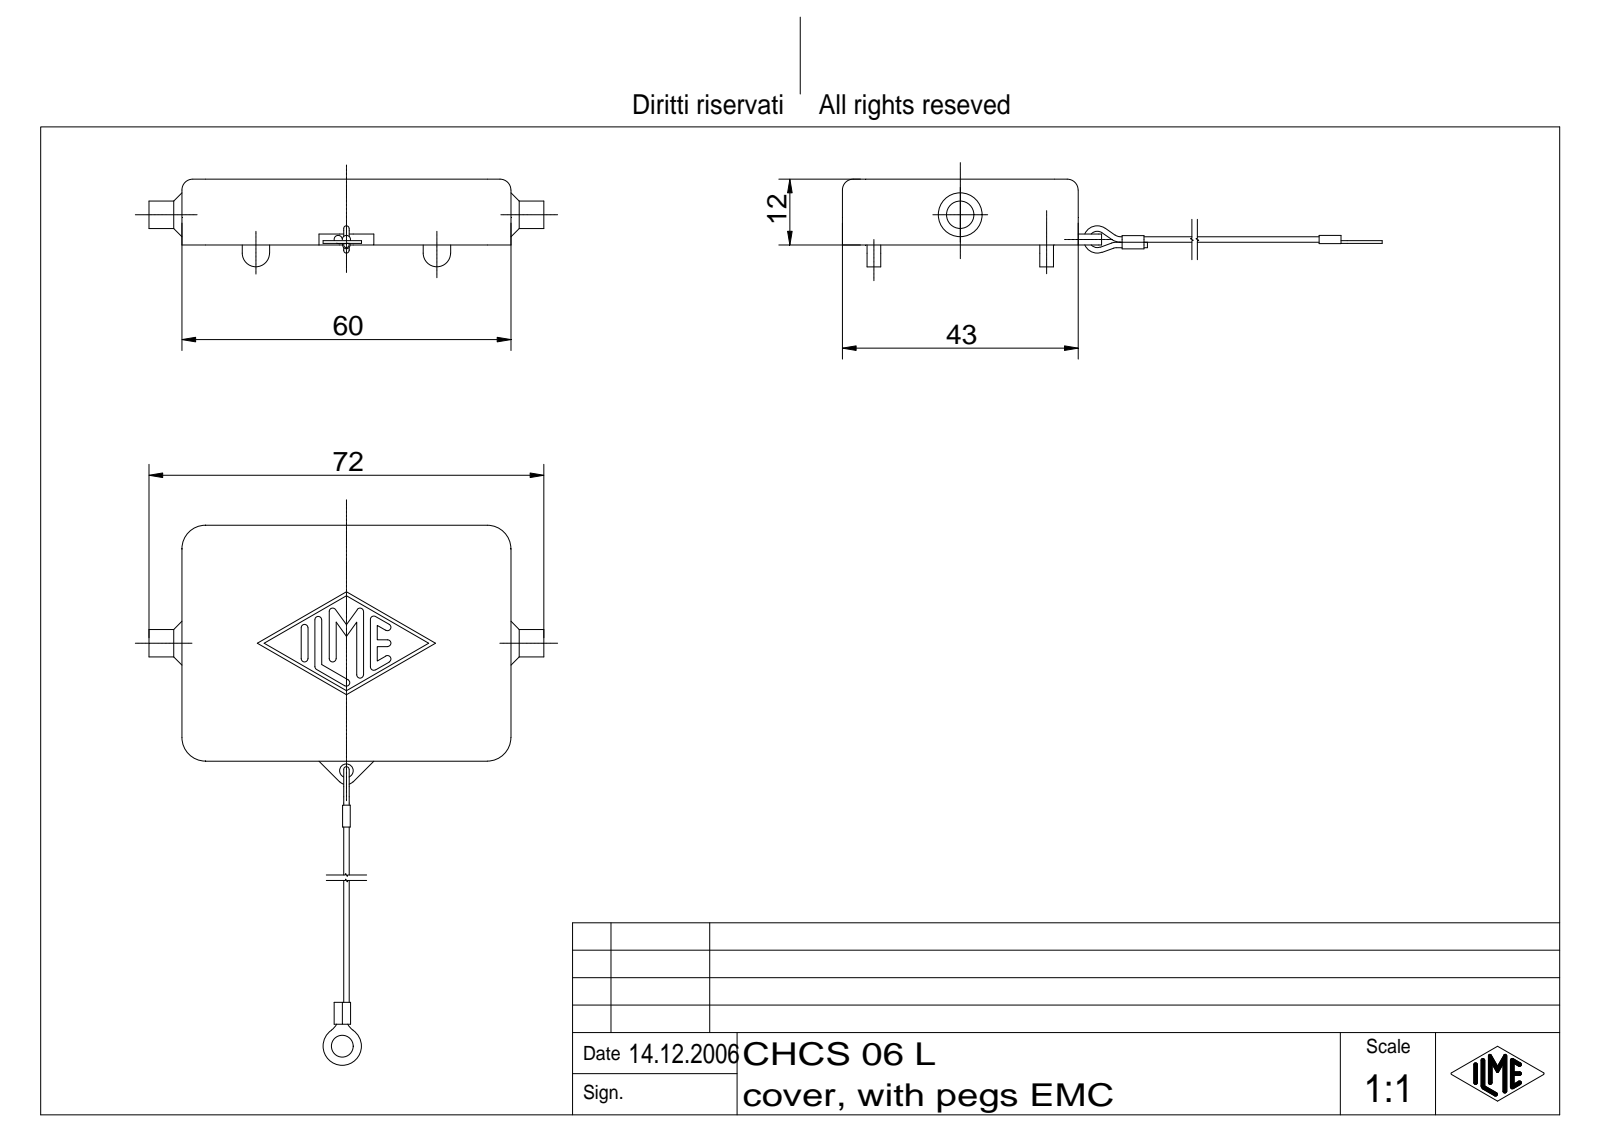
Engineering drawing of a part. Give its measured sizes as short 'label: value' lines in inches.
name: CHCS 06 L
written by: Autodesk Inventor 7 (AUTOMOTIVE_DESIGN)
unit: in
bodies: 2 solids, 176 faces (80 planar, 75 cylindrical, 21 other)
size: 5.807 × 2.835 × 0.63
volume: 0.979 in³; area: 15.44 in²
holes: 1× ⌀0.098, 1× ⌀0.157
bosses: 4× ⌀0.039, 1× ⌀0.276, 1× ⌀0.197
rounds: 14× R0.024, 8× R0.079, 4× R0.169, 2× R0.028, 2× R0.03, 2× R0.098, 2× R0.118, 1× R0.069
face distances: 0.118, 0.177, 0.472, 0.354, 1.516, 2.185, 1.693, 1.339, 2.362, 2.008
hole spacings: 3.907
